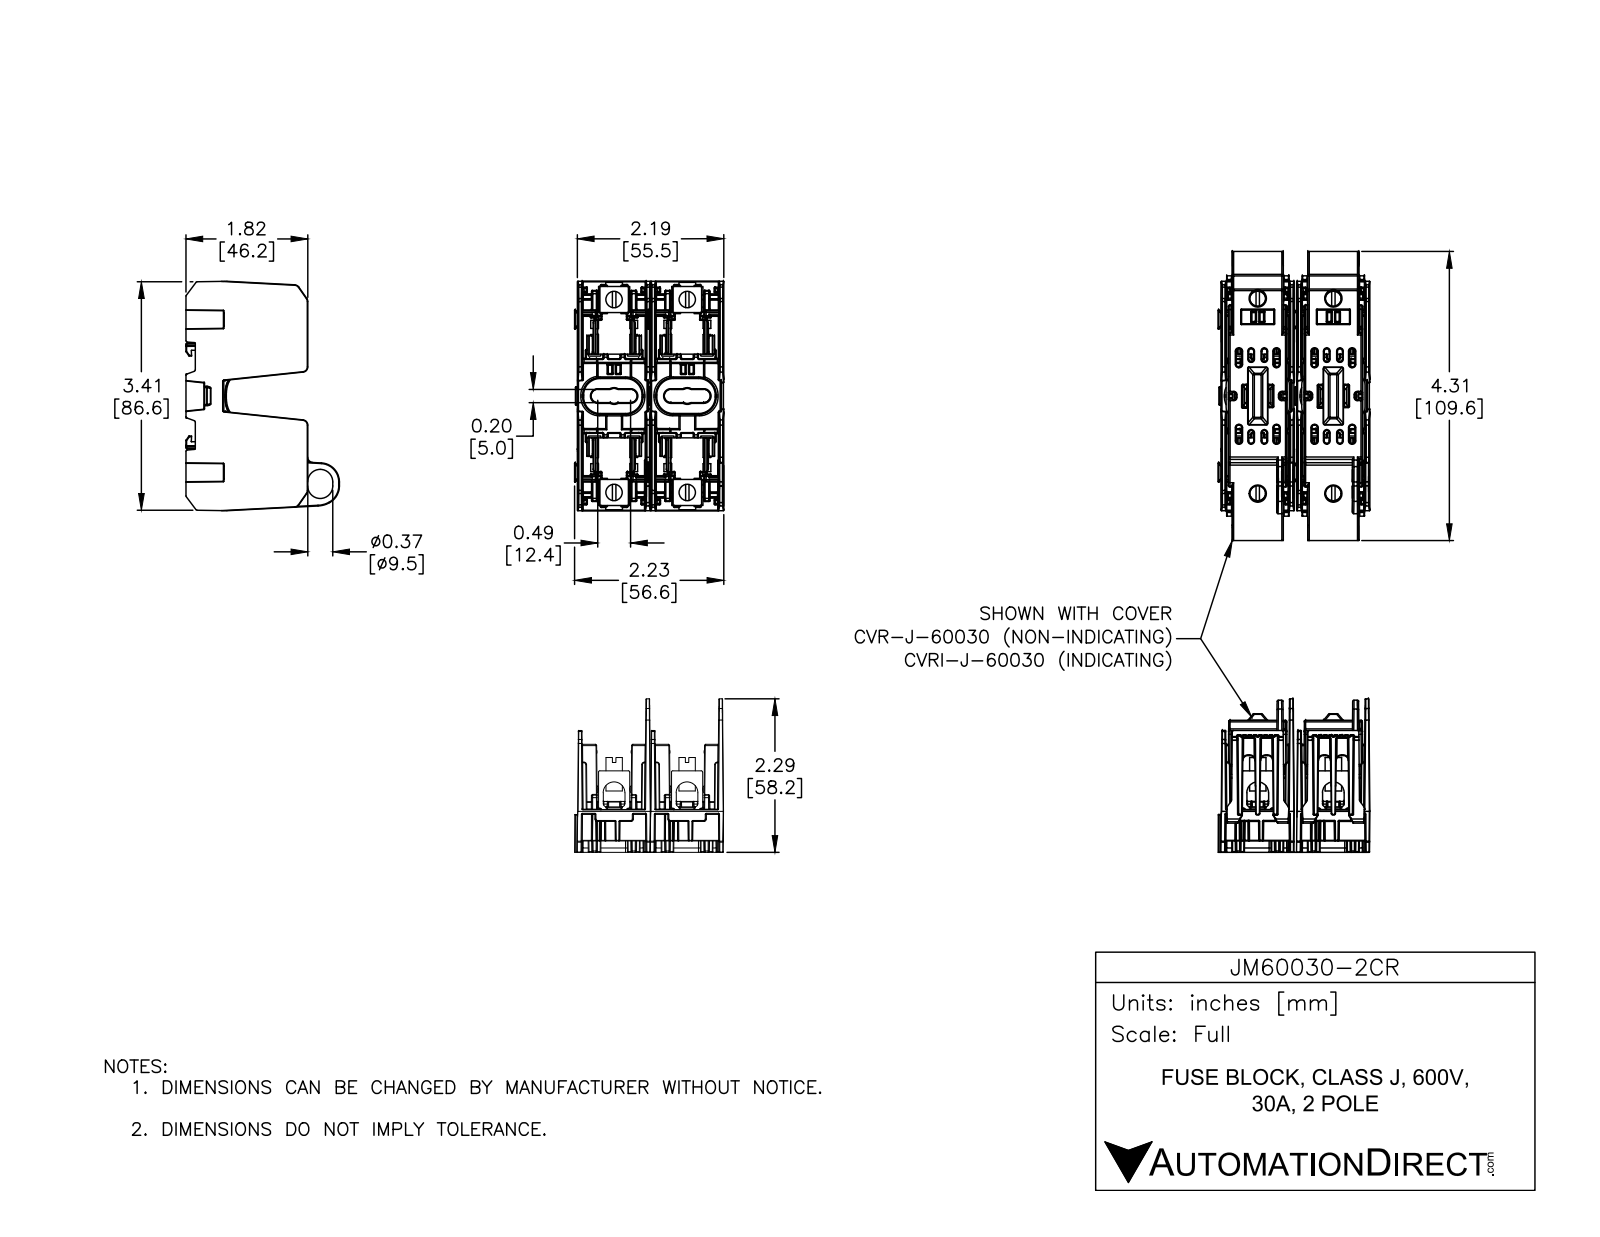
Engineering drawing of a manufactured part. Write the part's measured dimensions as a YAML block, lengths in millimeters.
part_name: "JM60030-1CR; JM60030-2CR"
step_written_by: "SolidWorks 2016 (AUTOMOTIVE_DESIGN)"
units: millimeters
bodies: {solids: 26, faces: 6186, planar: 1562, cylindrical: 2658, other: 1966}
overall_size: [87.2, 58.2, 56.5]
volume: 64750
surface_area: 66580
round_holes:
  - {diameter: 5.7, count: 4}
  - {diameter: 6.2, count: 4}
round_bosses_or_shafts:
  - {diameter: 6.2, count: 4}
partial_cylinders:
  - {radius: 0.3, count: 760}
  - {radius: 0.2, count: 591}
  - {radius: 0.5, count: 87}
  - {radius: 1, count: 60}
  - {radius: 0.1, count: 48}
  - {radius: 0.5, count: 16}
  - {radius: 1.5, count: 12}
  - {radius: 2, count: 11}
face_to_face_distances: [27.7, 25.7, 0.6, 25.8, 1.9, 53.4, 1.9, 27.7, 53.4, 1.7]
hole_center_spacings: [27.7, 31.5, 15.1, 15.1, 42.9, 51.1, 58, 58]
